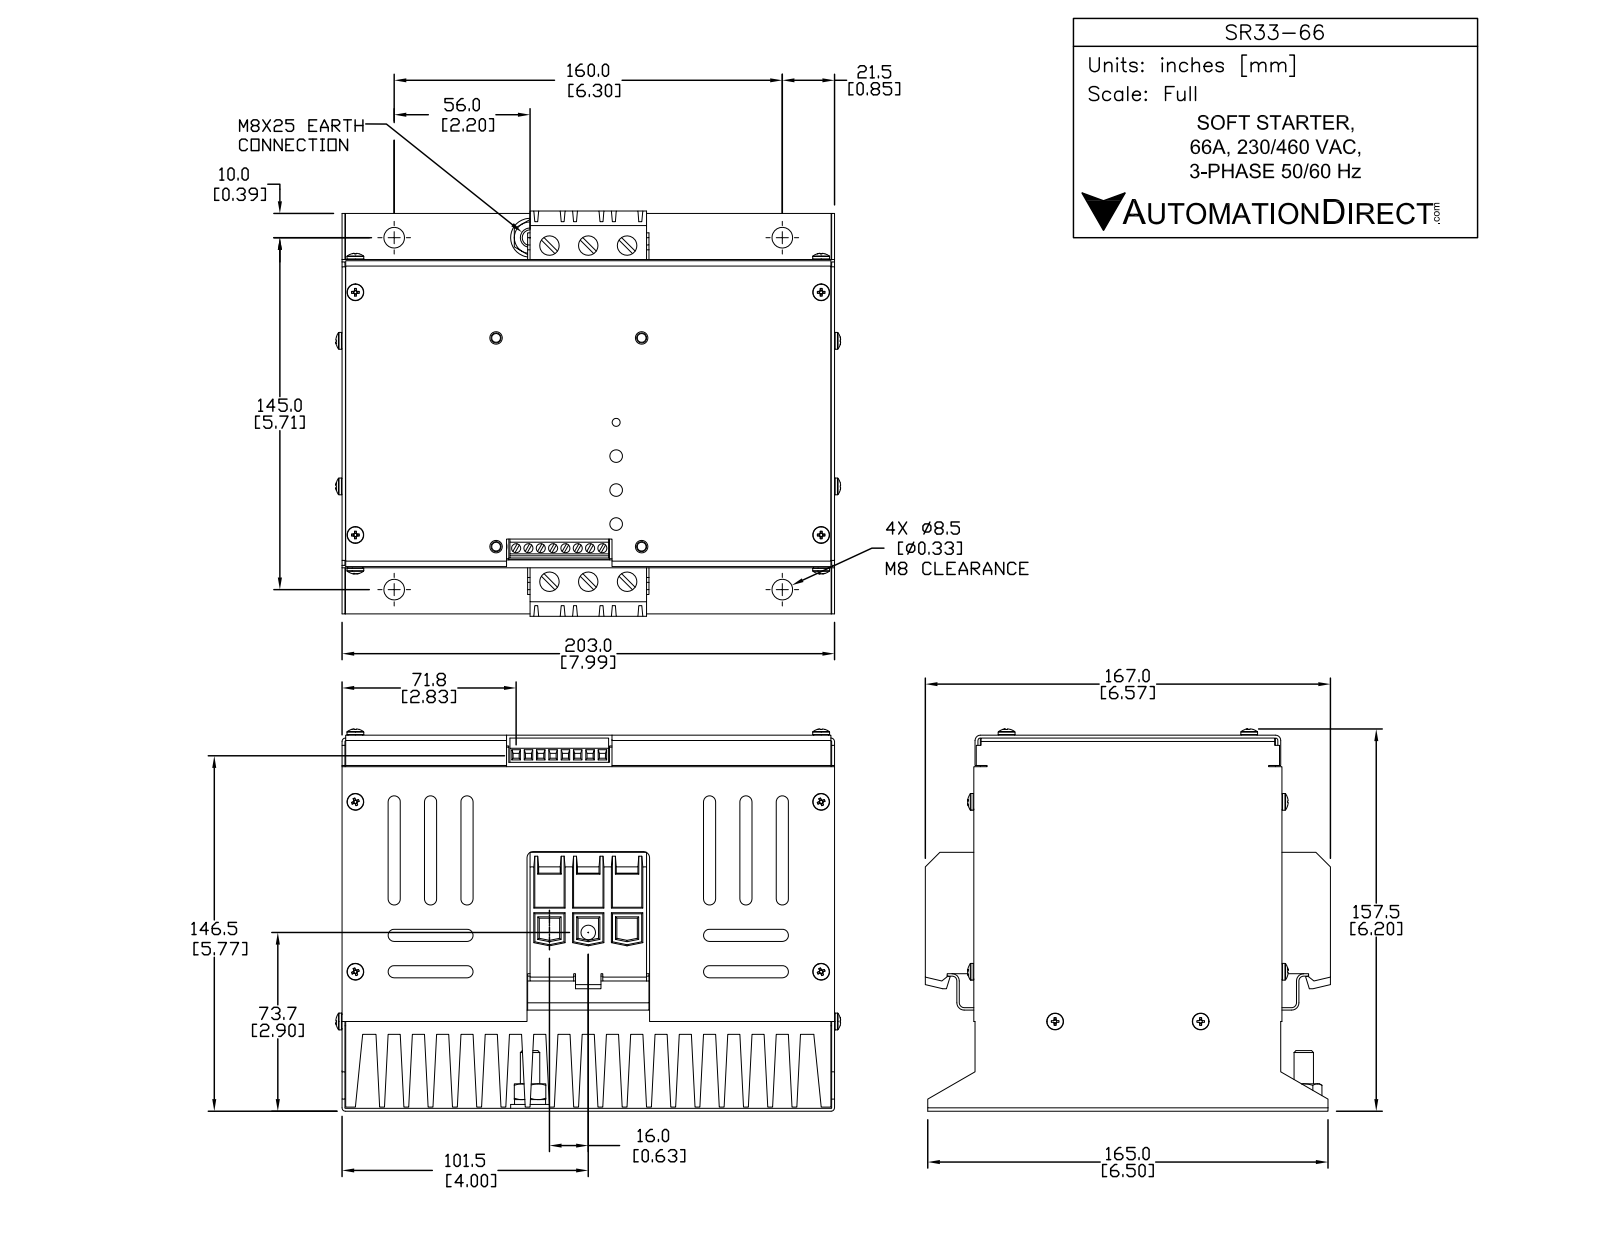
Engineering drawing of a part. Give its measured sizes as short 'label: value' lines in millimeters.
name: SR33-66
written by: SolidWorks 2013 (AUTOMOTIVE_DESIGN)
unit: mm
bodies: 1 solid, 838 faces (611 planar, 153 cylindrical, 74 other)
size: 203 × 165 × 158
volume: 3 299 000 mm³; area: 489 547 mm²
holes: 8× ⌀3.82, 6× ⌀5, 4× ⌀8.5
bosses: 8× ⌀6.9, 1× ⌀12, 1× ⌀6
rounds: 24× R0.5, 20× R2.5, 8× R2, 6× R1
face distances: 9.99, 19.98, 29.97, 39.96, 49.95, 59.94, 69.93, 79.92, 89.91, 99.9
hole spacings: 4.92, 9.84, 14.76, 15, 19.68, 65.12, 80.1, 95.08
